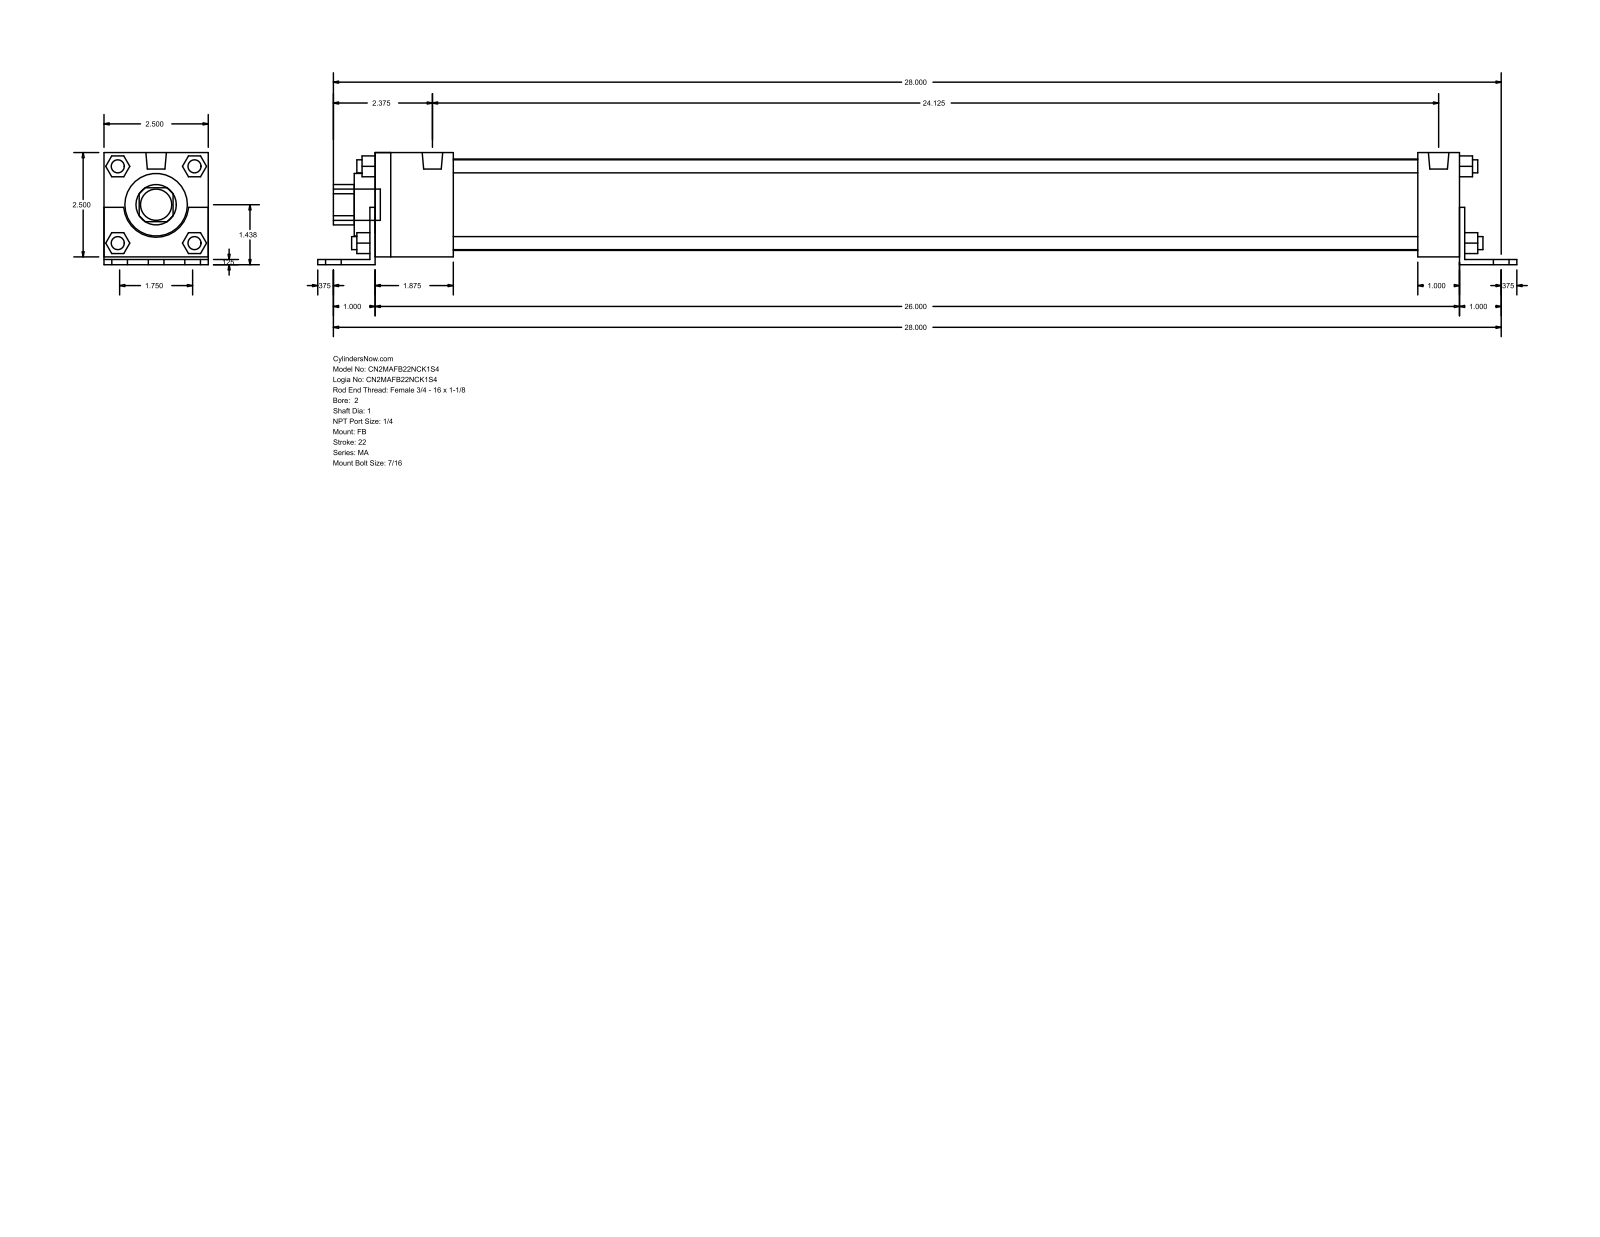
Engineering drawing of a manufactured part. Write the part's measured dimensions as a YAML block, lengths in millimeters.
part_name: "MA_FB__0200_1"
step_written_by: "GSSL Pune (CONFIG_CONTROL_DESIGN)"
units: millimeters
bodies: {solids: 0, faces: 140, planar: 105, cylindrical: 35, other: 0}
overall_size: [730.25, 68.26, 63.5]
round_holes:
  - {diameter: 25.4, count: 1}
  - {diameter: 38.1, count: 1}
  - {diameter: 55.63, count: 1}
round_bosses_or_shafts:
  - {diameter: 7.94, count: 8}
  - {diameter: 11.11, count: 6}
  - {diameter: 12.49, count: 2}
  - {diameter: 19.05, count: 1}
partial_cylinders:
  - {radius: 12.29, count: 1}
  - {radius: 19.81, count: 1}
face_to_face_distances: [63.5, 3.17, 4.76, 68.26, 1.59, 65.09, 12.7, 3.18, 660.4, 663.58]
